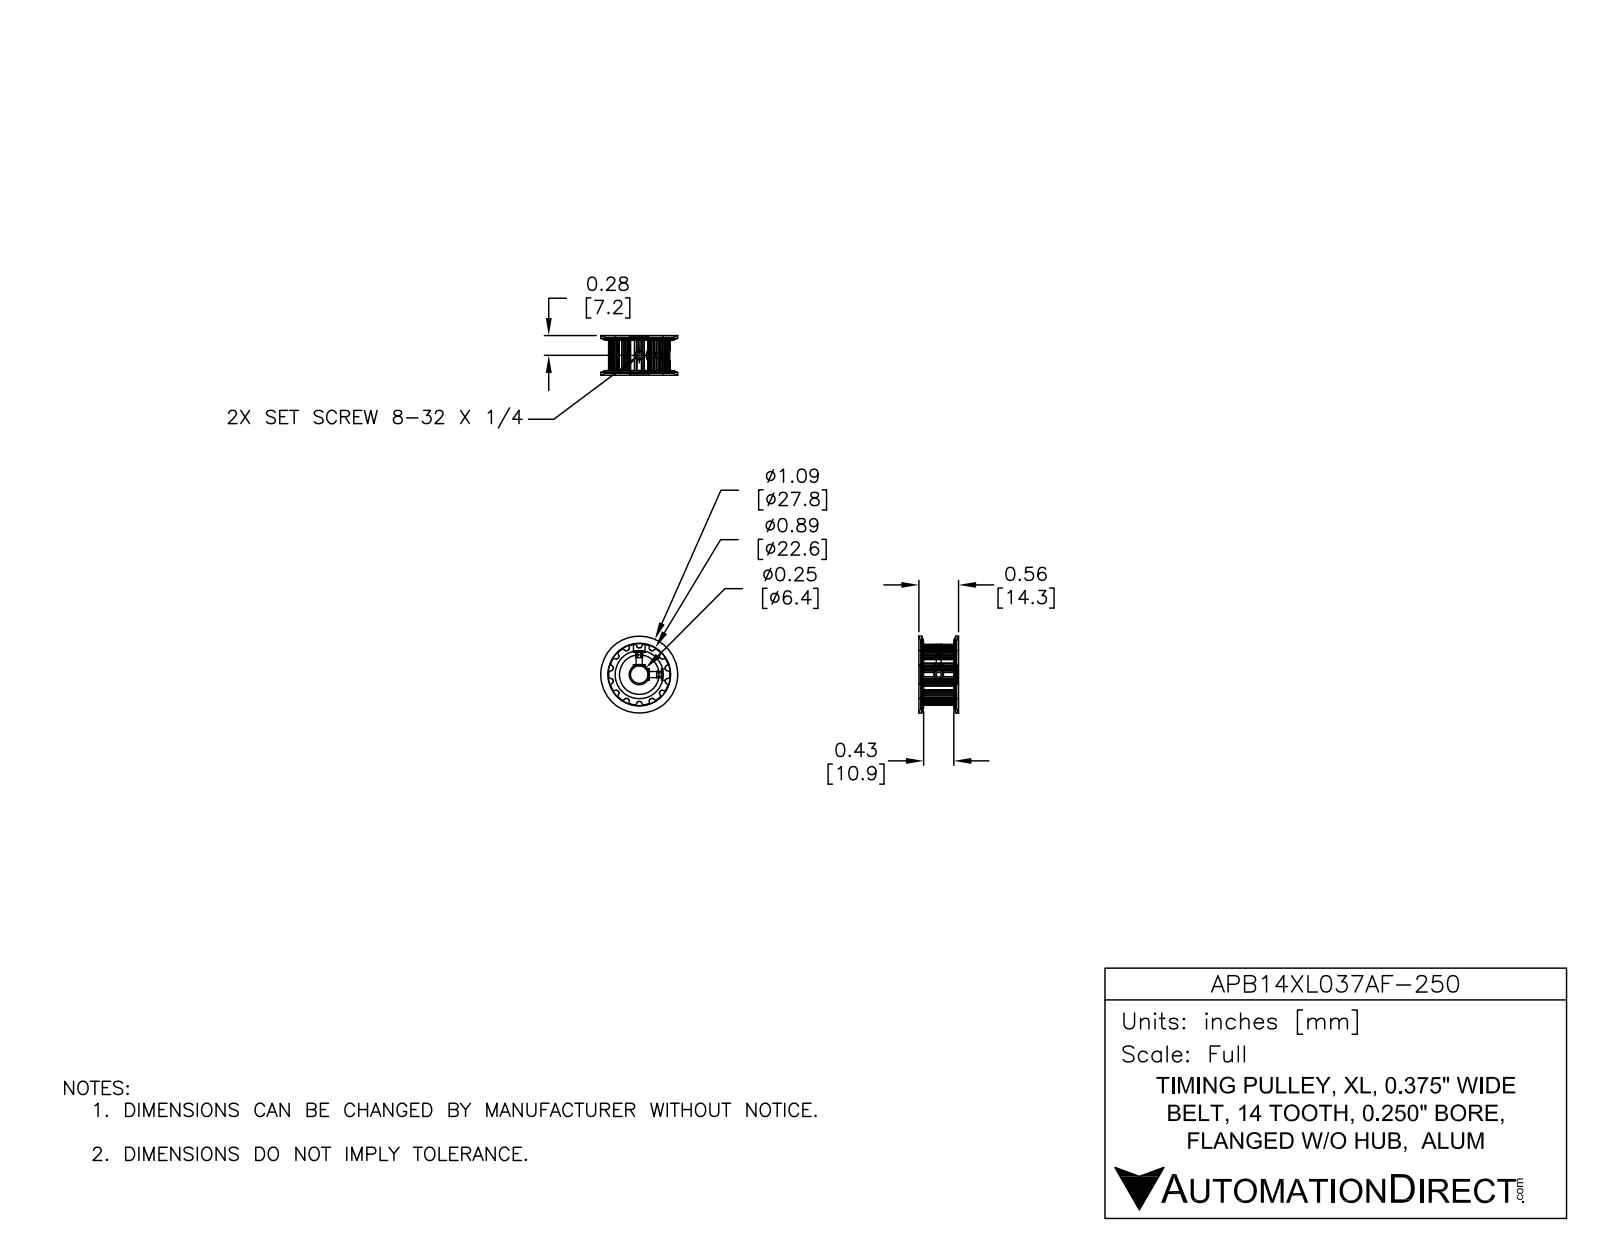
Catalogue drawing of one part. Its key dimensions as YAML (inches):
part_name: "APB14XL037AF-250"
step_written_by: "SolidWorks 2014 (AUTOMOTIVE_DESIGN)"
units: inches
bodies: {solids: 1, faces: 174, planar: 53, cylindrical: 101, other: 20}
overall_size: [1.094, 1.094, 0.563]
volume: 0.275
surface_area: 4.995
round_holes:
  - {diameter: 0.088, count: 2}
  - {diameter: 0.125, count: 1}
  - {diameter: 0.125, count: 1}
  - {diameter: 0.25, count: 1}
round_bosses_or_shafts:
  - {diameter: 0.496, count: 1}
partial_cylinders:
  - {radius: 0.015, count: 56}
  - {radius: 0.381, count: 1}
face_to_face_distances: [0.5, 0.031, 0.531, 0.063, 0.469, 0.275, 0.871, 0.563, 0.437, 0.275]
